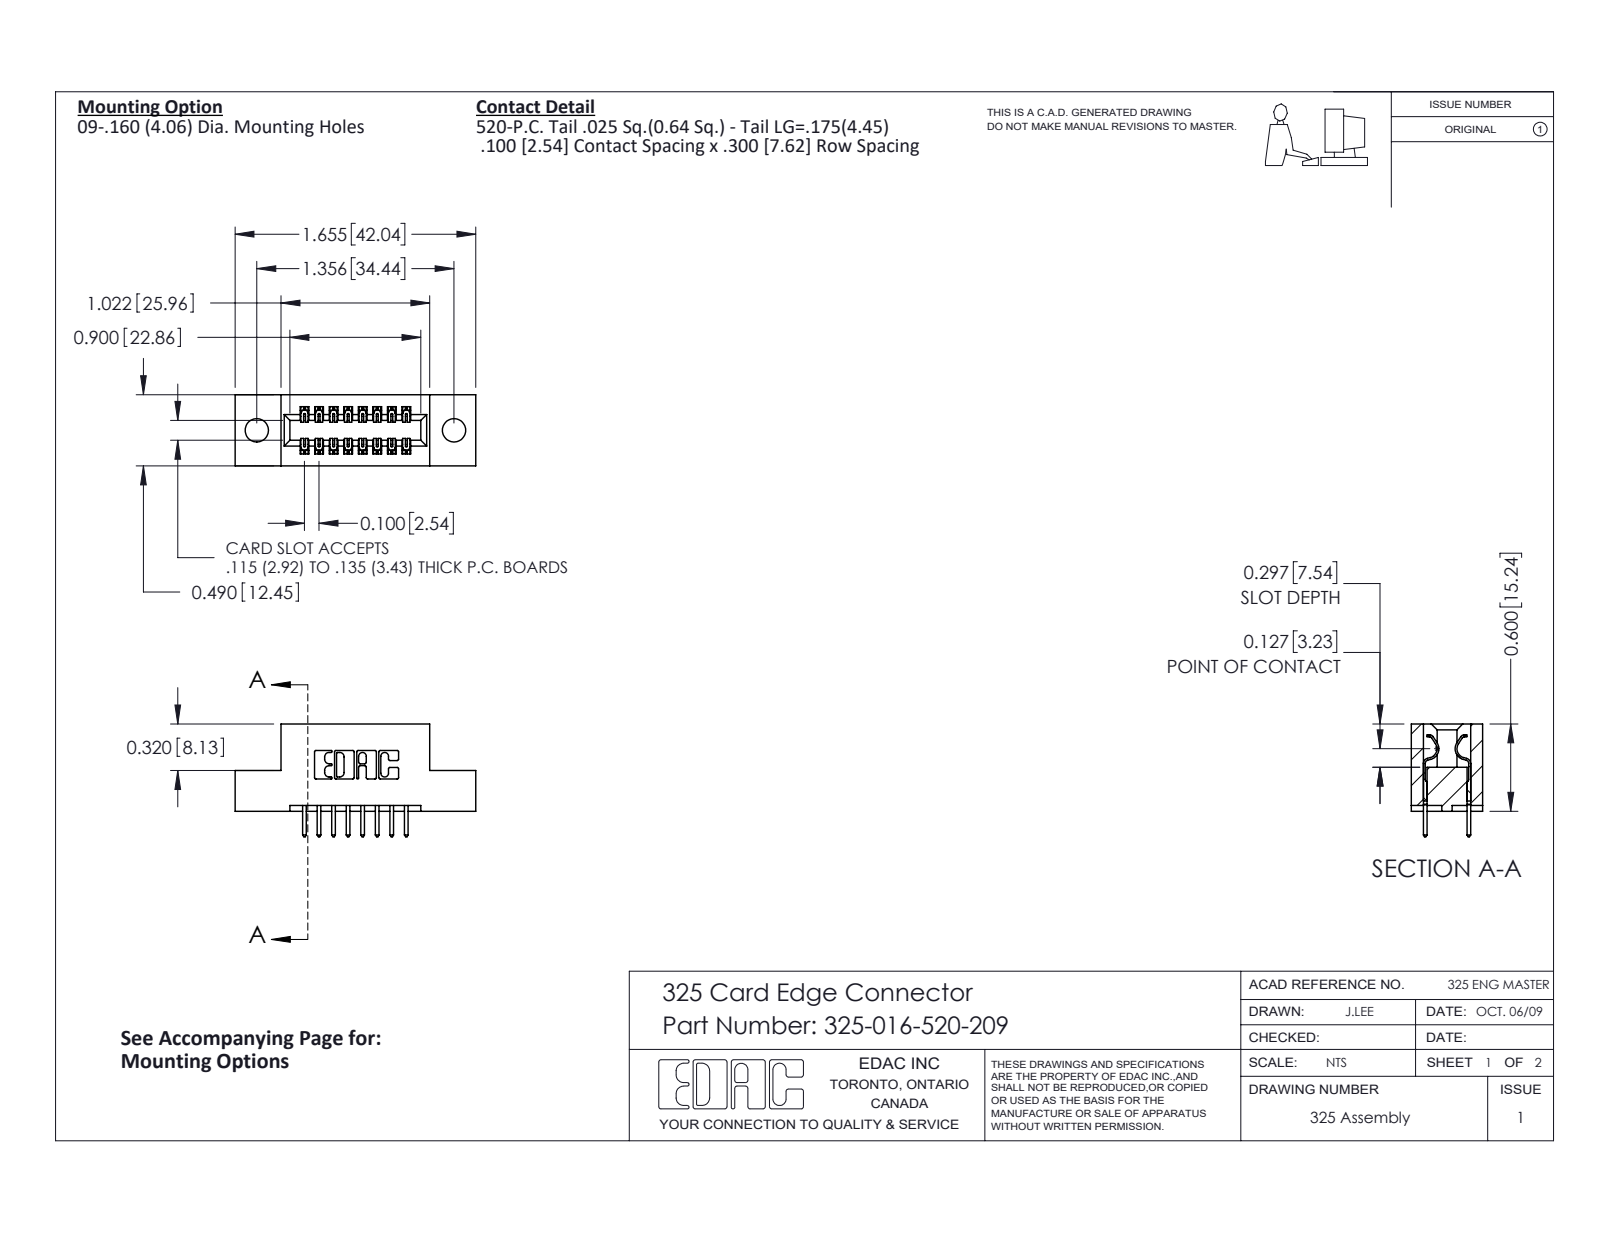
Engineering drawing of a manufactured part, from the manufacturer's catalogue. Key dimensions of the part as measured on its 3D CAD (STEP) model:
Part name (STEP PRODUCT): 325 Part_.160 TH; 325-292-001_325-293-120; 325-016-520-209
STEP written by: SolidWorks 2016 (CONFIG_CONTROL_DESIGN)
Units: inches
Bodies: 17 solids, 946 faces (646 planar, 300 cylindrical, 0 other)
Overall size (bounding box): 1.655 × 0.775 × 0.49
Volume: 0.298 in³ · Surface area: 7.748 in²
Round holes (diameter × count): ⌀0.16 ×2
Partial cylindrical surfaces — rounded edges, fillets, slot ends (radius × count): R0.006 ×24, R0.01 ×22, R0.01 ×16, R0.007 ×6, R0.031 ×6, R0.026 ×3, R0.014 ×2, R0.022 ×2
Main face-to-face distances: 0.3, 0.1, 0.2, 0.083, 0.407, 0.04, 0.49, 0.06, 0.4, 0.6
Hole centre spacings: 1.356
